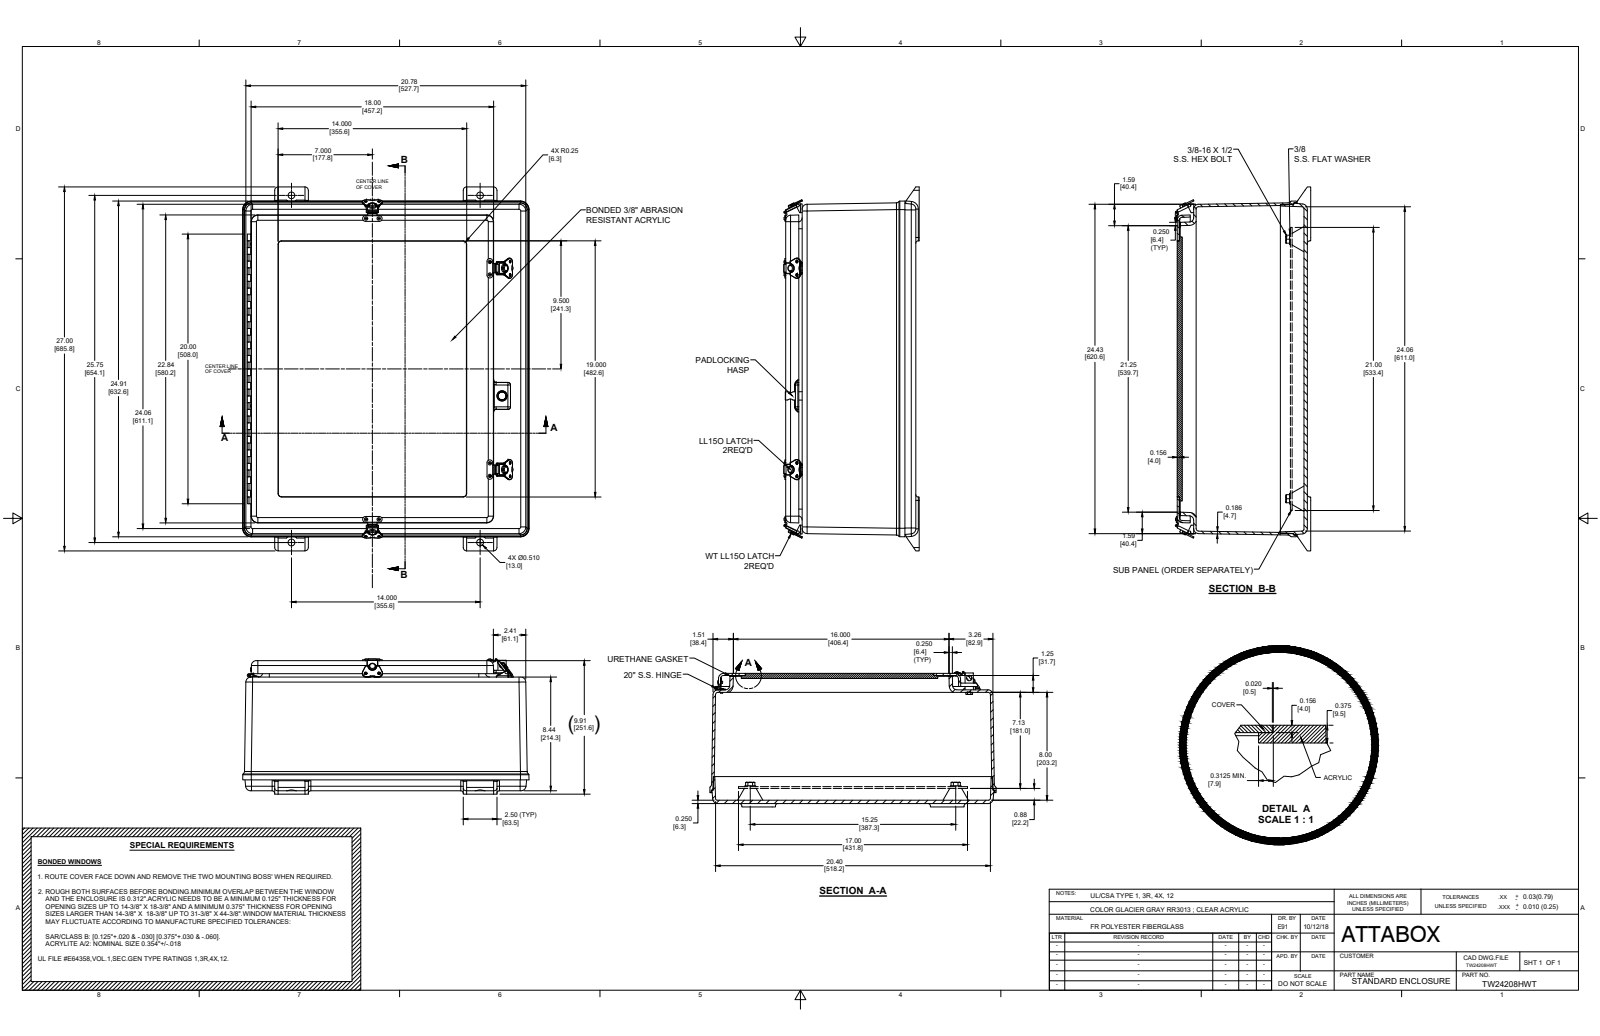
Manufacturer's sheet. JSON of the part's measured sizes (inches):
{"part_name": "TW24208HWT", "step_written_by": "SolidWorks 2018 (AUTOMOTIVE_DESIGN)", "units": "inches", "bodies": {"solids": 59, "faces": 1597, "planar": 606, "cylindrical": 614, "other": 377}, "overall_size": [27, 21.25, 10.055], "volume_in3": 473, "surface_area_in2": 4441, "round_holes": [[0.13, 32], [0.063, 16], [0.138, 8], [0.187, 8], [0.065, 6], [0.307, 4], [0.563, 4], [0.156, 3], [0.065, 2], [0.135, 2], [0.5, 2], [0.51, 2]], "round_bosses_or_shafts": [[0.14, 16], [0.297, 8], [0.5, 4], [0.2, 3], [0.25, 1], [0.201, 1], [0.135, 1]], "partial_cylinders_radius": [[0.01, 101], [0.25, 28], [0.187, 18], [0.03, 16], [0.312, 16], [0.375, 16], [0.5, 12], [0.125, 10]], "face_to_face_distances": [0.25, 0.186, 9.658, 9.408, 9.283, 9.033, 0.375, 0.186, 0.156, 9.502], "hole_center_spacings": [6.5, 12, 0.751, 0.937, 1, 1.512, 3.309, 14.938]}
